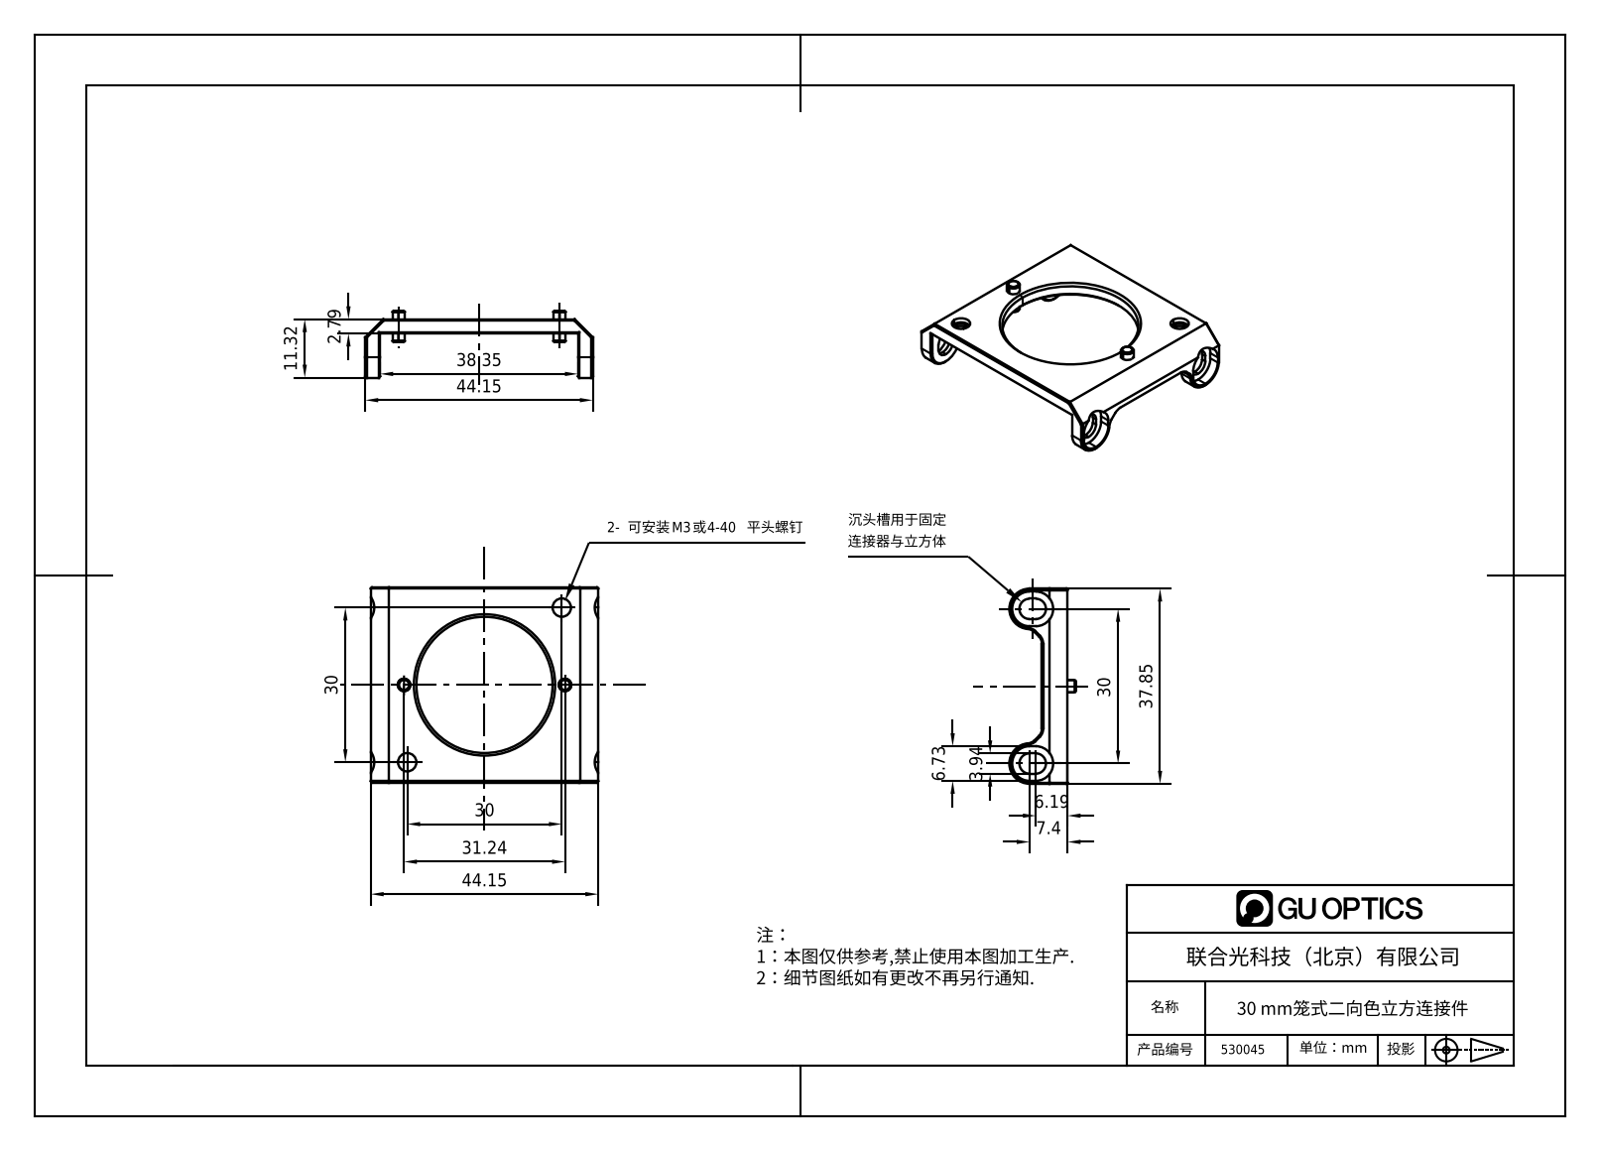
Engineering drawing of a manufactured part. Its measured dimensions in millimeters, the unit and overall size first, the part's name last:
Units: millimetres
Overall size (bounding box): 44.15 × 37.85 × 12.93
Round holes (diameter × count): ⌀3.56 ×2, ⌀6.2 ×2, ⌀26.42 ×1
Round bosses / shafts (diameter × count): ⌀2.4 ×2
Partial cylindrical surfaces — rounded edges, fillets, slot ends (radius × count): R1.97 ×4, R2 ×4, R3.37 ×4, R3.92 ×2
Main face-to-face distances: 2.79, 38.36, 37.86, 0.89, 39.25, 2, 2.89, 41.25, 42.14, 2.21
Hole centre spacings: 21.21, 42.43
Bodies: 0 solids, 166 faces (68 planar, 54 cylindrical, 44 other)
Part name (STEP PRODUCT): 2.2.7.33_L30F-BL2_30 mm笼式二向色立方连接件
STEP written by: SolidWorks 2018 (AUTOMOTIVE_DESIGN)
